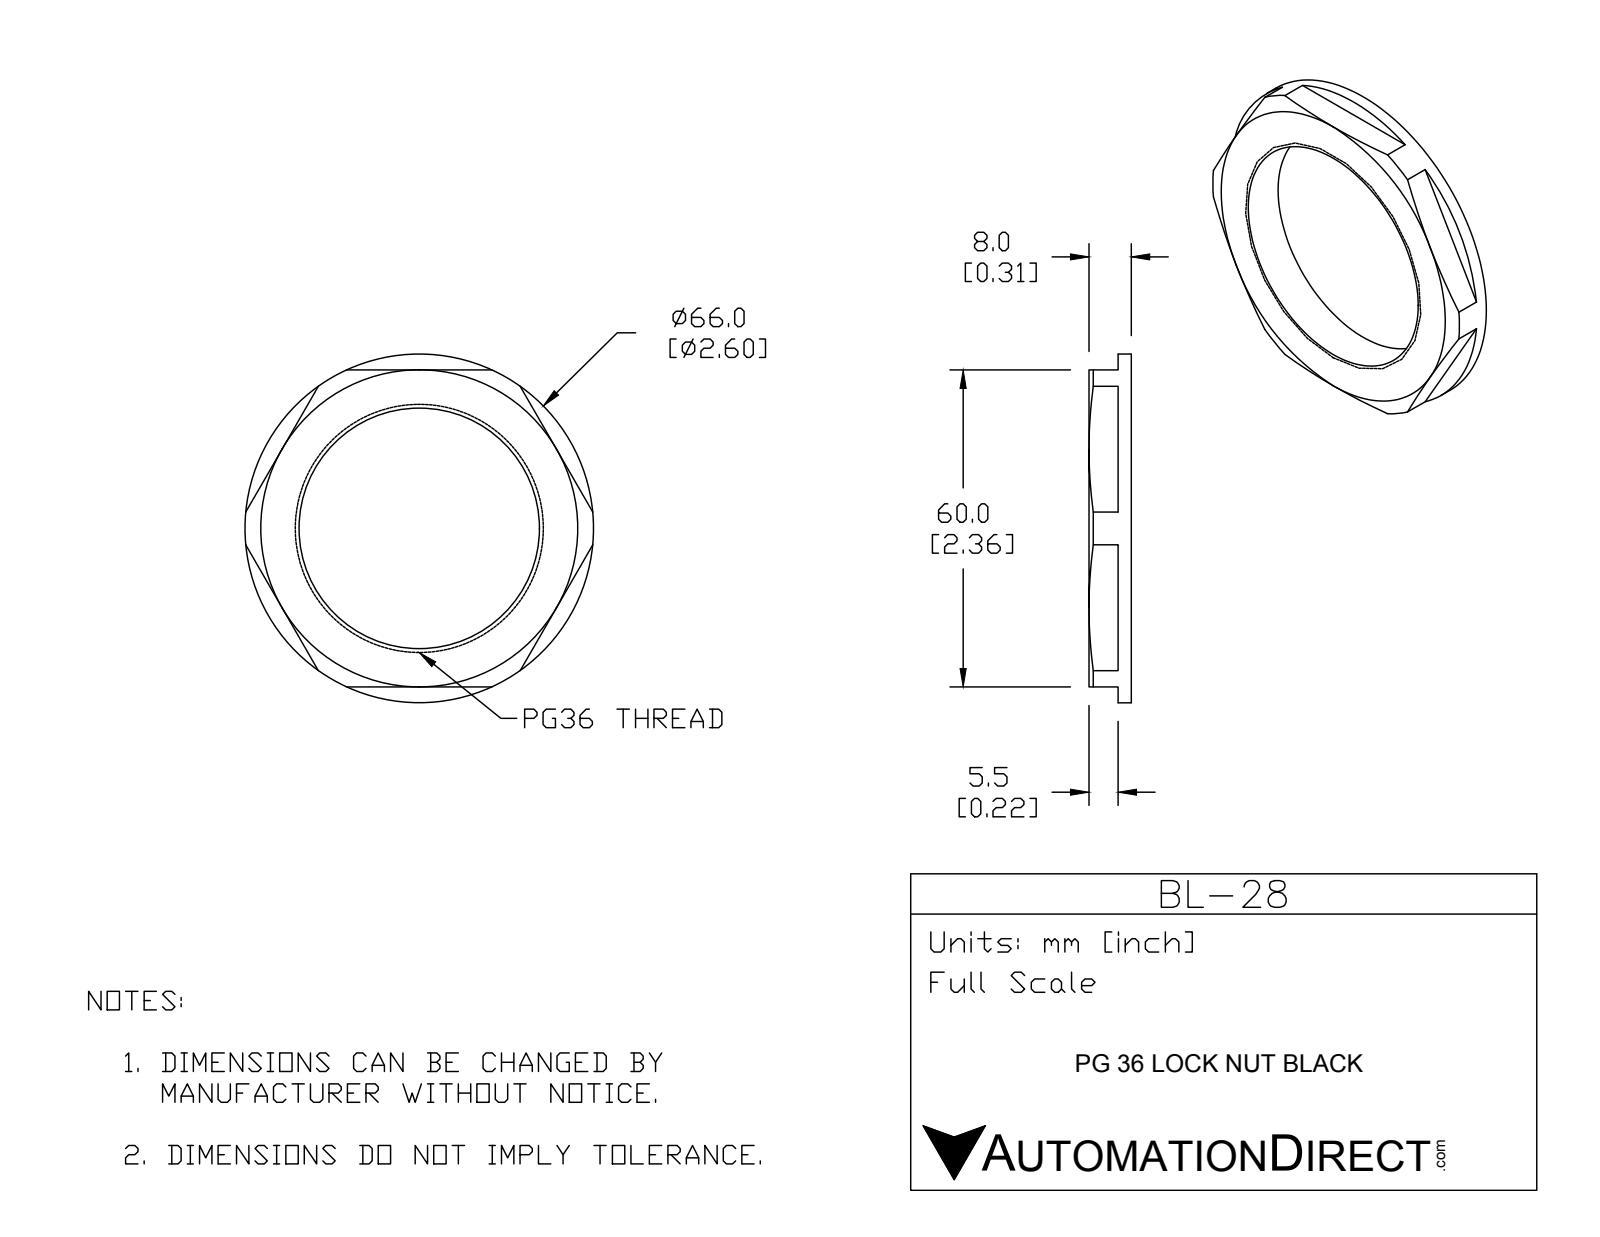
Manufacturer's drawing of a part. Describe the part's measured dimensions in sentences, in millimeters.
The part is named "BL-28". Its 3-D file was written by "SolidWorks 2015 (CONFIG_CONTROL_DESIGN)". It is 1 solid with 33 faces: 17 planar, 10 cylindrical and 6 other. Overall it measures 66 by 66 by 8 millimeters. Its volume is 12 447 cubic millimeters and its surface area 6 303 square millimeters. Round holes: 3 of diameter 1.5, 1 of diameter 45.5. Round bosses or shafts: 1 of diameter 66. The main face-to-face distances are 8, 60, 2.5, 5.5, 2.2, 7.7. The hole center spacings are 31.55, 54.64, 31.54, 54.65.
